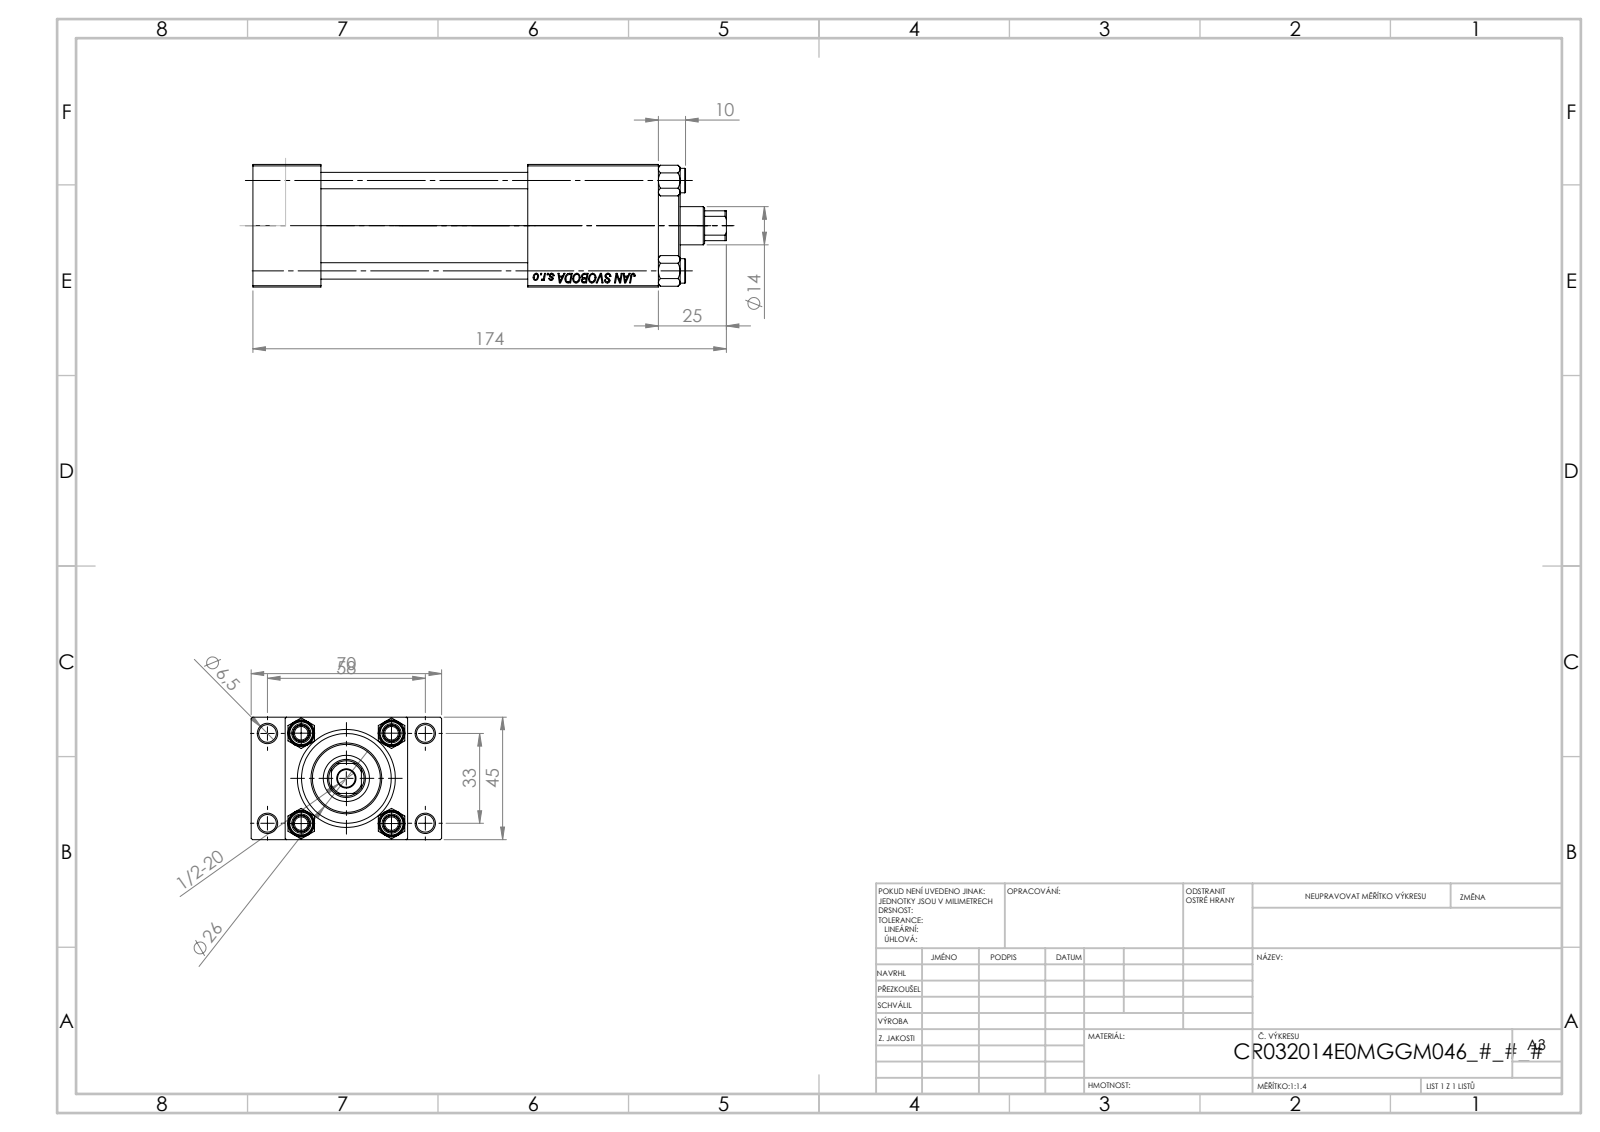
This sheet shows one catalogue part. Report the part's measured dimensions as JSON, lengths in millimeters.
{"part_name": "NUT_M5_E; V215_VC_A; V215CR_VCP_E; V215CR_TYCINKA_E (+1 more)", "step_written_by": "SolidWorks 2019 (CONFIG_CONTROL_DESIGN)", "units": "millimeters", "bodies": {"solids": 11, "faces": 1136, "planar": 497, "cylindrical": 87, "other": 552}, "overall_size": [174, 70, 45], "volume_mm3": 235593, "surface_area_mm2": 84894, "round_holes": [[6.5, 5], [6, 4], [7, 2], [13.16, 2], [20, 2], [14, 1], [17, 1], [24, 1], [32, 1], [33, 1]], "round_bosses_or_shafts": [[9, 4], [38, 1], [26, 1]], "partial_cylinders_radius": [[6.5, 1]], "face_to_face_distances": [45, 25, 12.5, 57.5, 149, 124, 70, 101, 76, 48], "hole_center_spacings": [12.4, 23.48, 33.2, 33.37, 35.35, 45.6, 56.35, 33]}
